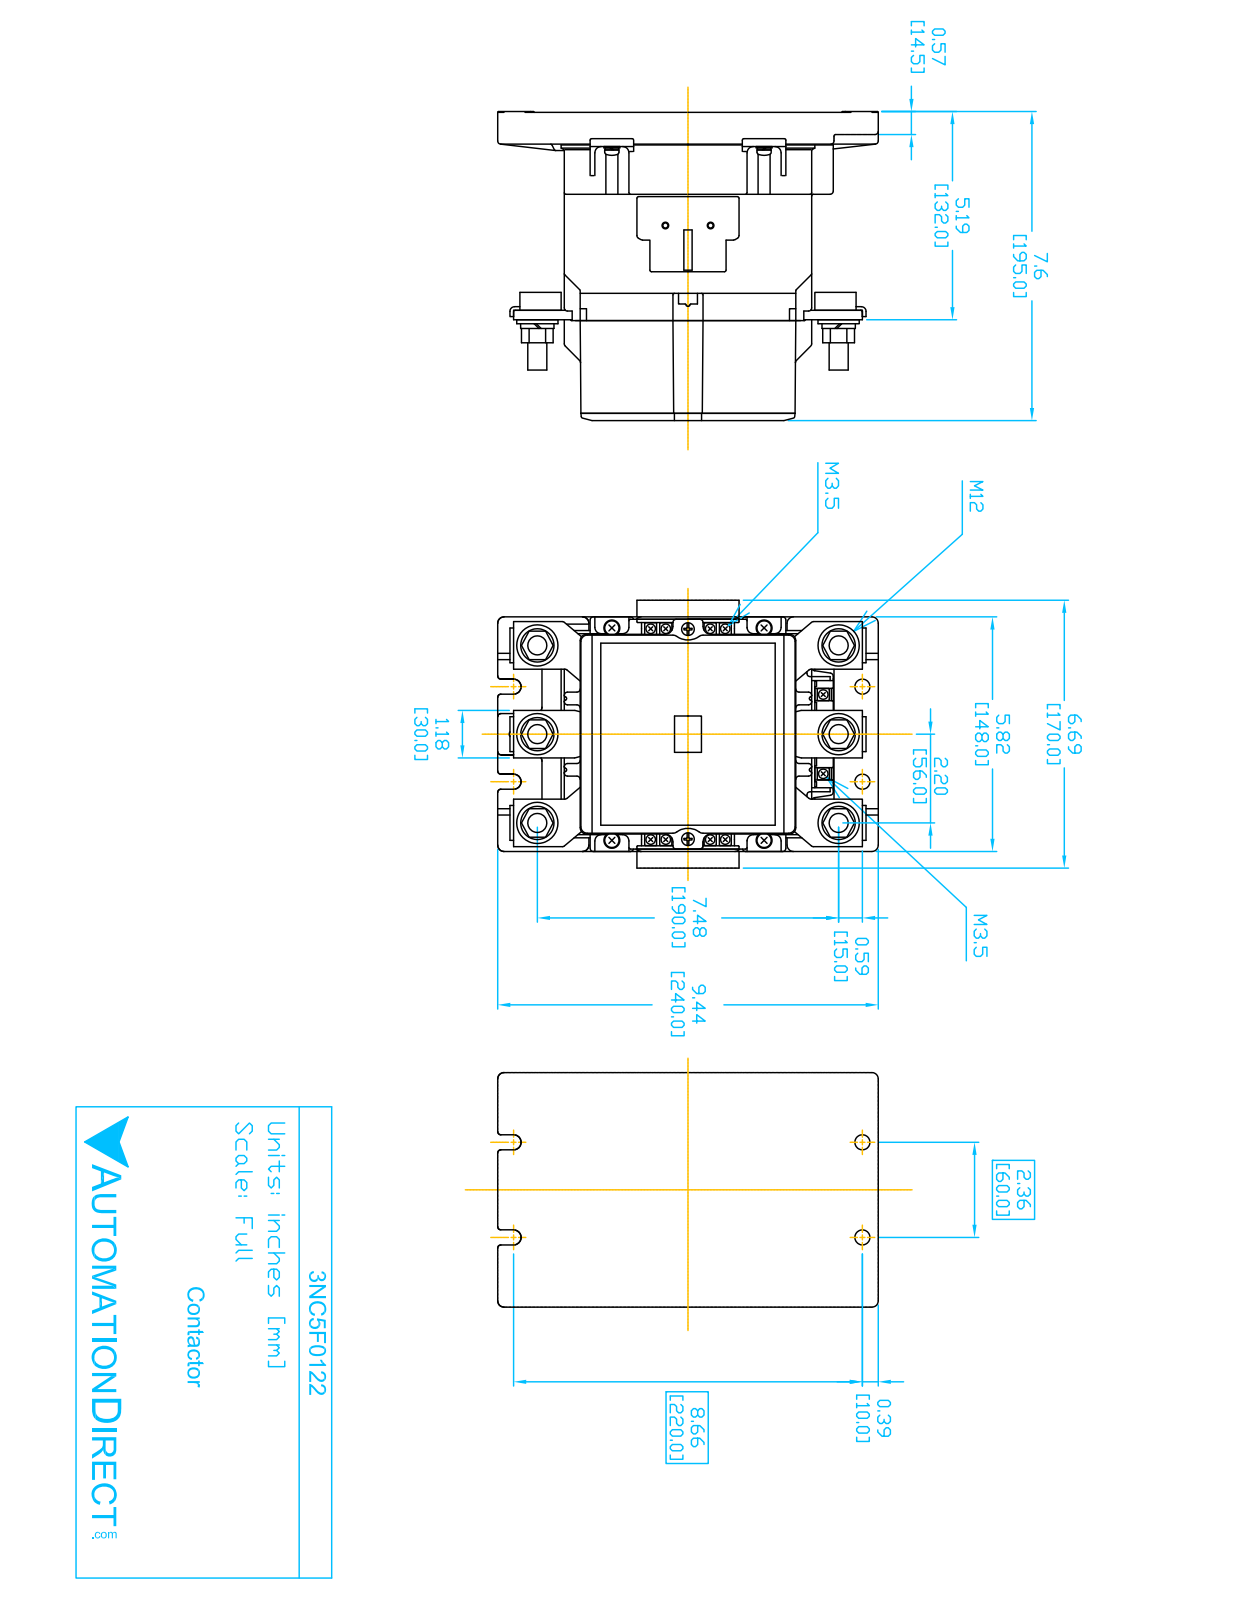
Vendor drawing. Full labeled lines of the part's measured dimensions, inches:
Part name (STEP PRODUCT): 3NC5F0122
STEP written by: SolidWorks 2018 (AUTOMOTIVE_DESIGN)
Units: inches
Bodies: 20 solids, 375 faces (261 planar, 114 cylindrical, 0 other)
Overall size (bounding box): 9.449 × 7.677 × 5.866
Volume: 256.1 in³ · Surface area: 431.1 in²
Round holes (diameter × count): ⌀0.472 ×6, ⌀0.315 ×2, ⌀0.394 ×2
Partial cylindrical surfaces — rounded edges, fillets, slot ends (radius × count): R0.079 ×26, R0.157 ×16, R0.039 ×12, R0.031 ×8, R0.197 ×6, R0.02 ×2
Main face-to-face distances: 4.528, 0.433, 4.961, 0.394, 5.748, 5.394, 3.15, 7.677, 0.827, 3.701
Hole centre spacings: 2.244, 3.765, 4.6, 6.181, 7.81, 7.48, 1.213, 1.324
